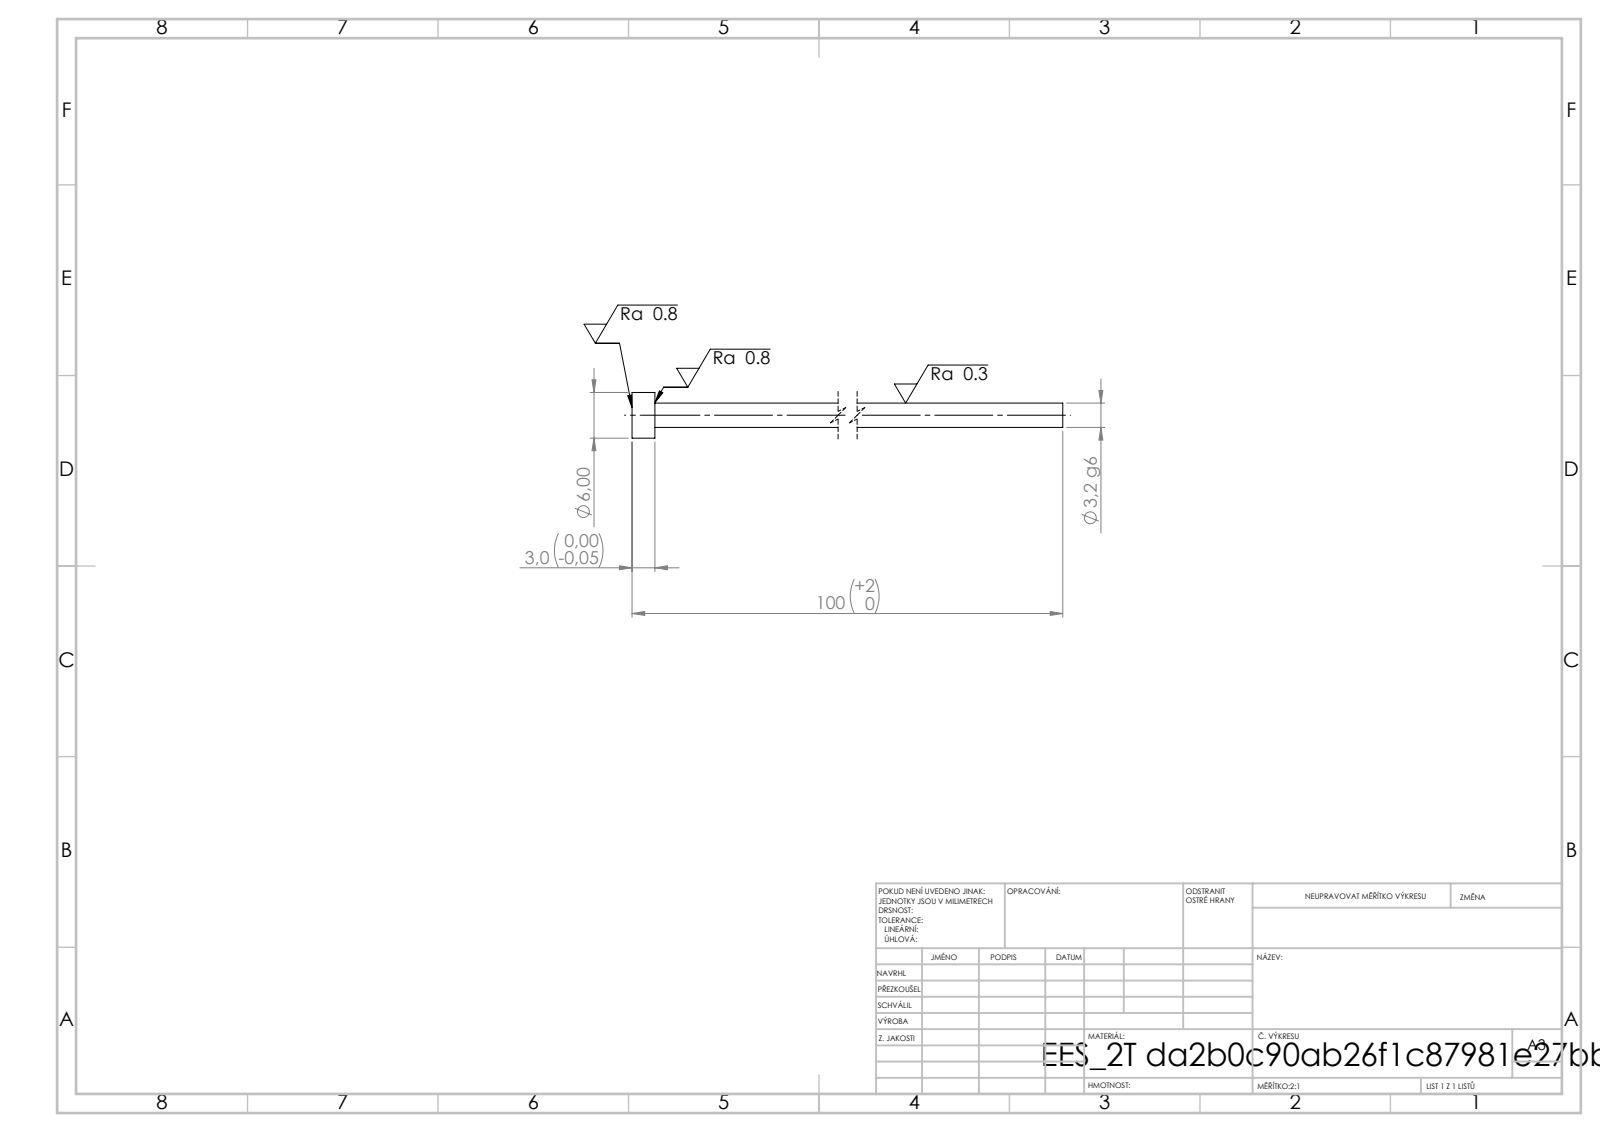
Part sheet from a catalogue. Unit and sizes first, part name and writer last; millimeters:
Units: millimetres
Overall size (bounding box): 100 × 6 × 6
Round bosses / shafts (diameter × count): ⌀6 ×1, ⌀3.2 ×1
Main face-to-face distances: 3, 100, 97
Volume: 865 mm³ · Surface area: 1 088 mm²
Bodies: 1 solid, 7 faces (3 planar, 4 cylindrical, 0 other)
STEP written by: SolidWorks 2019 (CONFIG_CONTROL_DESIGN)
